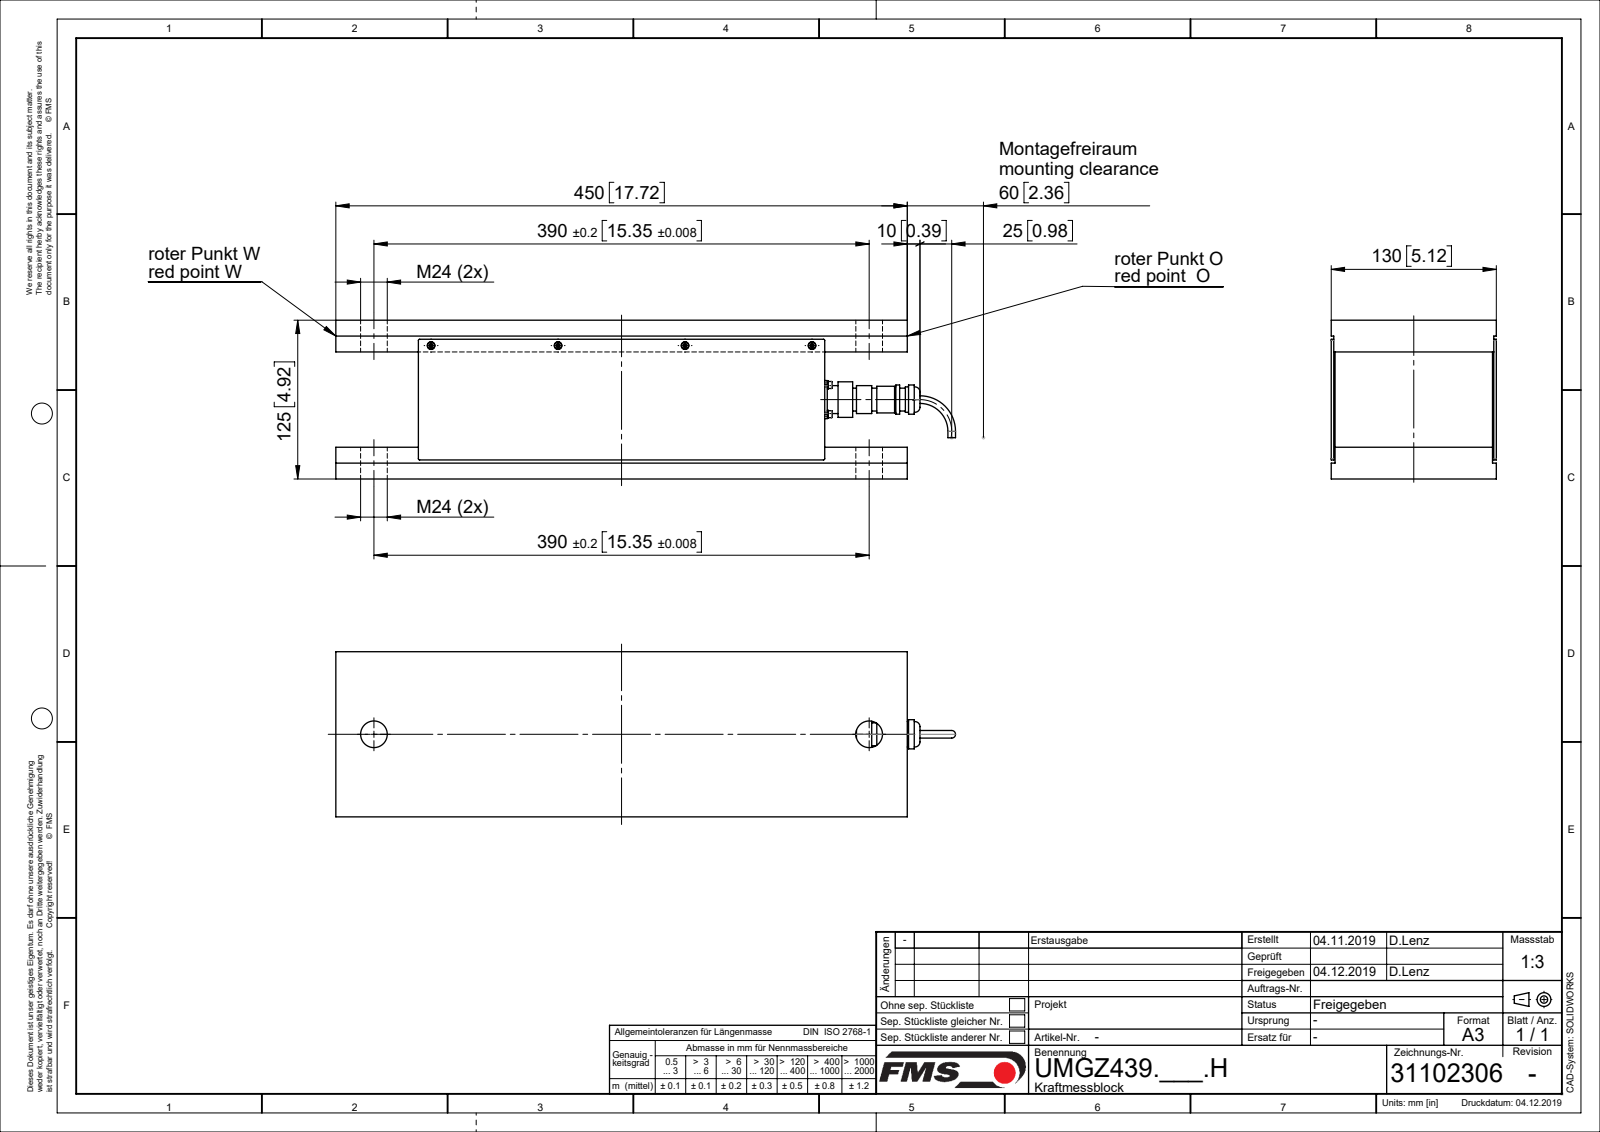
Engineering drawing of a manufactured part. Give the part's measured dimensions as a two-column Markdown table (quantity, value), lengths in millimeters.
| quantity | value |
| --- | --- |
| part name | 31102306; Federringe_DIN127A_M03; Se-Schr DIN7991_M3x8; 51132_01 (+3 more) |
| STEP written by | SolidWorks 2018 (CONFIG_CONTROL_DESIGN) |
| units | millimeters |
| bodies | 20 solids, 495 faces (209 planar, 194 cylindrical, 92 other) |
| overall size | 488 × 130 × 125 |
| volume | 4 782 000 mm³ |
| surface area | 518 788 mm² |
| round holes (diameter × count) | 2.5 × 8, 3.1 × 4, 3.2 × 4, 3.6 × 4, 6 × 4, 21 × 2 |
| round bosses / shafts (diameter × count) | 3 × 8, 6.2 × 4, 5.7 × 4, 5.5 × 4, 2.5 × 4, 28 × 1, 23 × 1, 22 × 1 |
| partial cylindrical surfaces (radius × count) | 1 × 4, 4 × 4, 12.5 × 4 |
| main face-to-face distances | 25, 125, 2, 128, 100, 130, 126, 105, 23, 103 |
| hole center spacings | 23, 100, 32.53, 200, 300, 390 |
